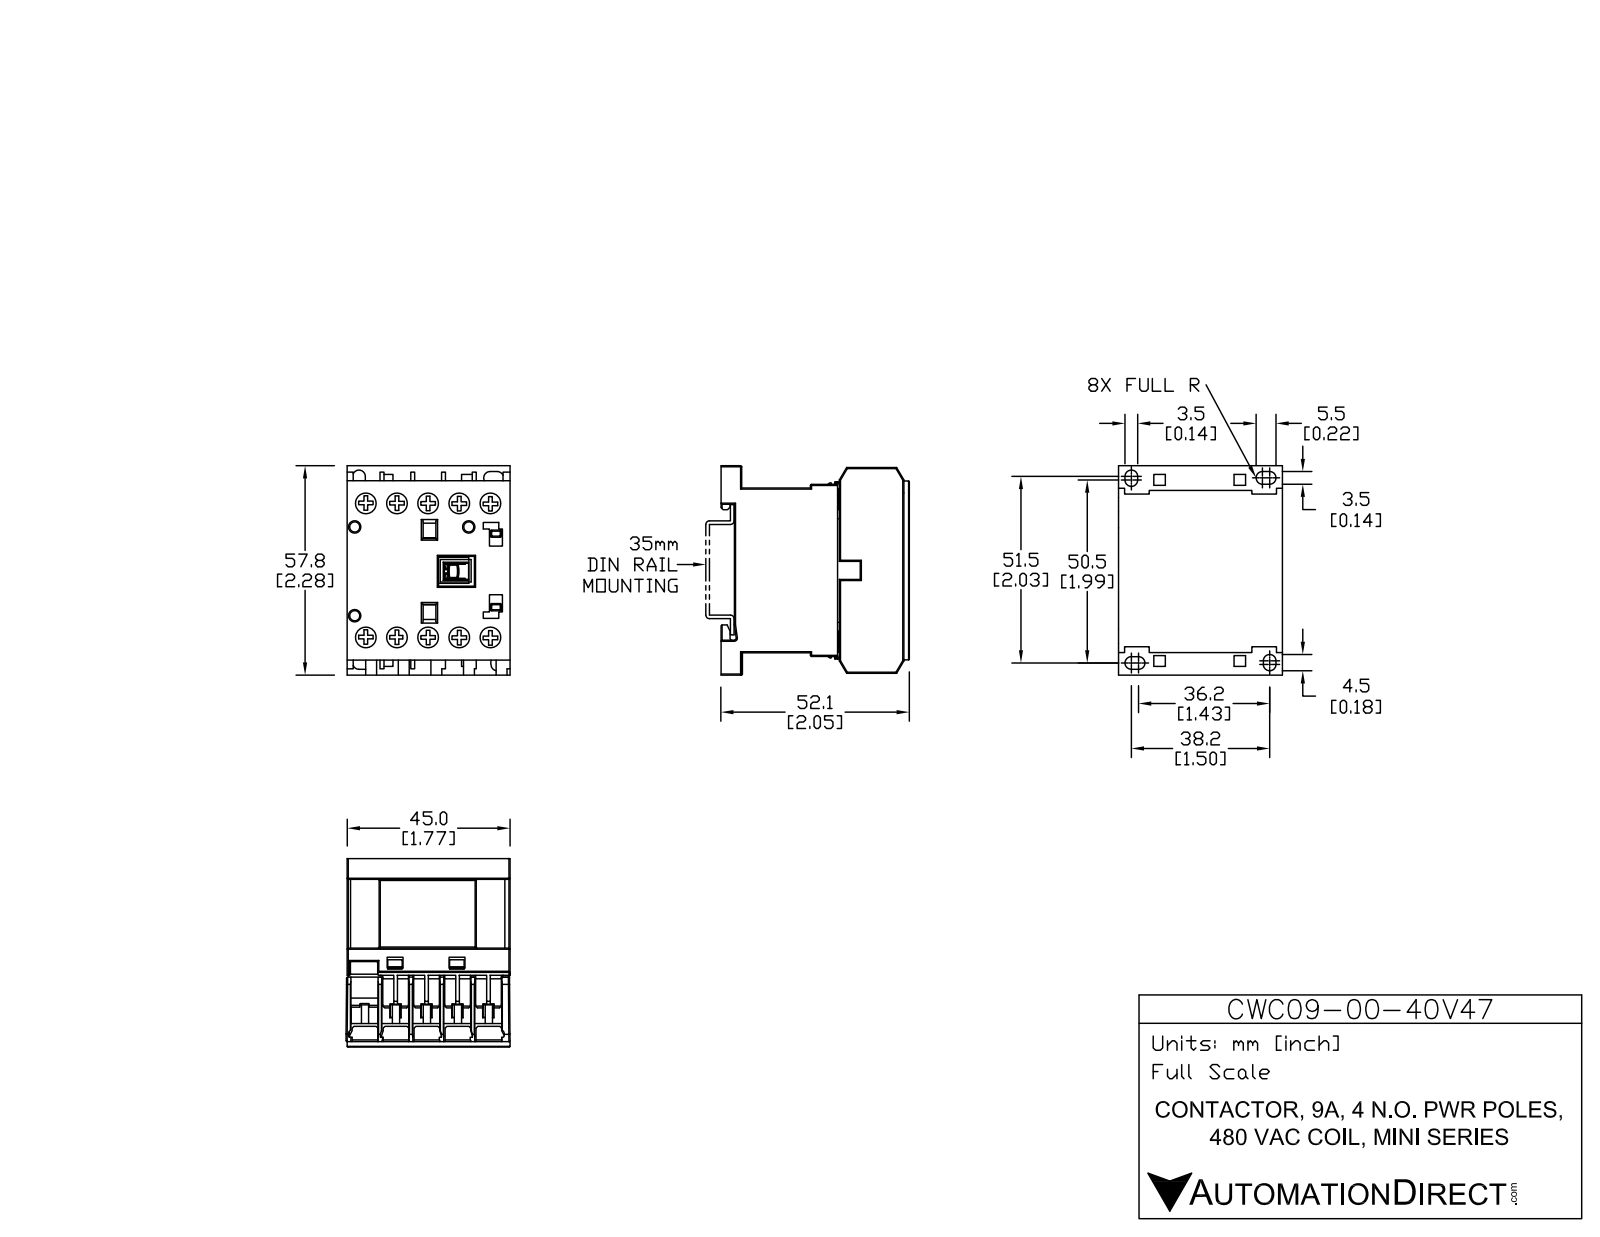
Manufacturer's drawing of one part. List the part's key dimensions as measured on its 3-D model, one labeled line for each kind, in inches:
Part name (STEP PRODUCT): CWC09-00-40V47
STEP written by: SolidWorks 2013 (AUTOMOTIVE_DESIGN)
Units: inches
Bodies: 15 solids, 535 faces (445 planar, 90 cylindrical, 0 other)
Overall size (bounding box): 2.285 × 2.052 × 1.801
Volume: 5.927 in³ · Surface area: 47.18 in²
Round holes (diameter × count): ⌀0.244 ×10, ⌀0.11 ×3
Round bosses / shafts (diameter × count): ⌀0.232 ×10
Partial cylindrical surfaces — rounded edges, fillets, slot ends (radius × count): R0.012 ×20, R0.068 ×6, R0.068 ×2, R0.013 ×1, R0.017 ×1, R0.022 ×1
Main face-to-face distances: 0.325, 1.791, 0.049, 0.65, 0.374, 0.217, 0.699, 0.202, 0.419, 0.276
Hole centre spacings: 0.337, 1.494, 0.673, 1.603, 1.455, 1.01, 1.771, 0.272
